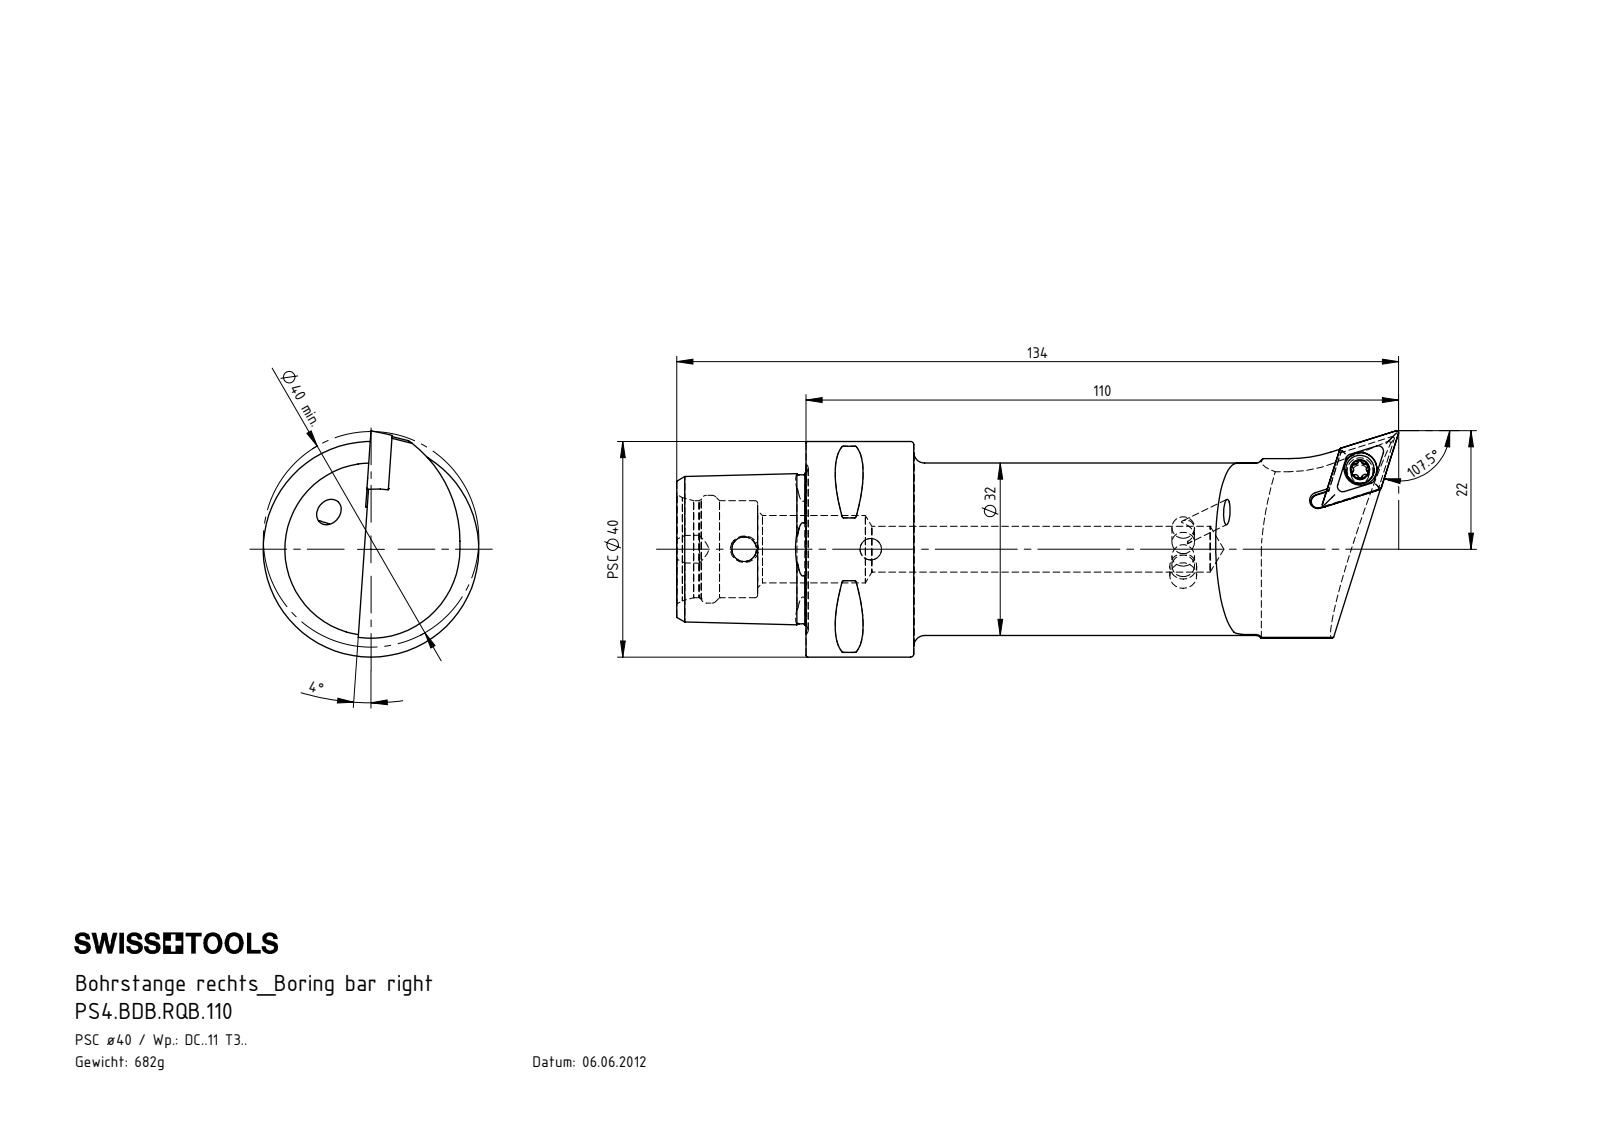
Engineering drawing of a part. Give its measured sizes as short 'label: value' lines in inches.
name: KVT_MB_600_050; WCB-ER2.001.009_A; DCMT11T304; PS4-BDB.RQB.110_A (+1 more)
written by: SolidWorks 2017 (AUTOMOTIVE_DESIGN)
unit: in
bodies: 5 solids, 295 faces (53 planar, 73 cylindrical, 169 other)
size: 5.276 × 1.654 × 1.575
volume: 5.288 in³; area: 30.58 in²
holes: 2× ⌀0.157, 2× ⌀0.165, 1× ⌀0.13, 1× ⌀0.173, 1× ⌀0.181, 1× ⌀0.24, 1× ⌀0.335, 1× ⌀0.492, 1× ⌀0.709, 1× ⌀0.787
bosses: 1× ⌀1.575, 1× ⌀1.26, 1× ⌀0.207, 1× ⌀0.197, 1× ⌀0.157
rounds: 8× R0.012, 6× R0.013, 6× R0.023, 2× R0.118, 1× R0.049, 1× R0.65, 1× R0.906, 1× R1.024
face distances: 0.787, 0.945, 1.732, 0.144, 0.611, 1.39, 0.591, 0.354, 1.142, 0.937
hole spacings: 0.925
